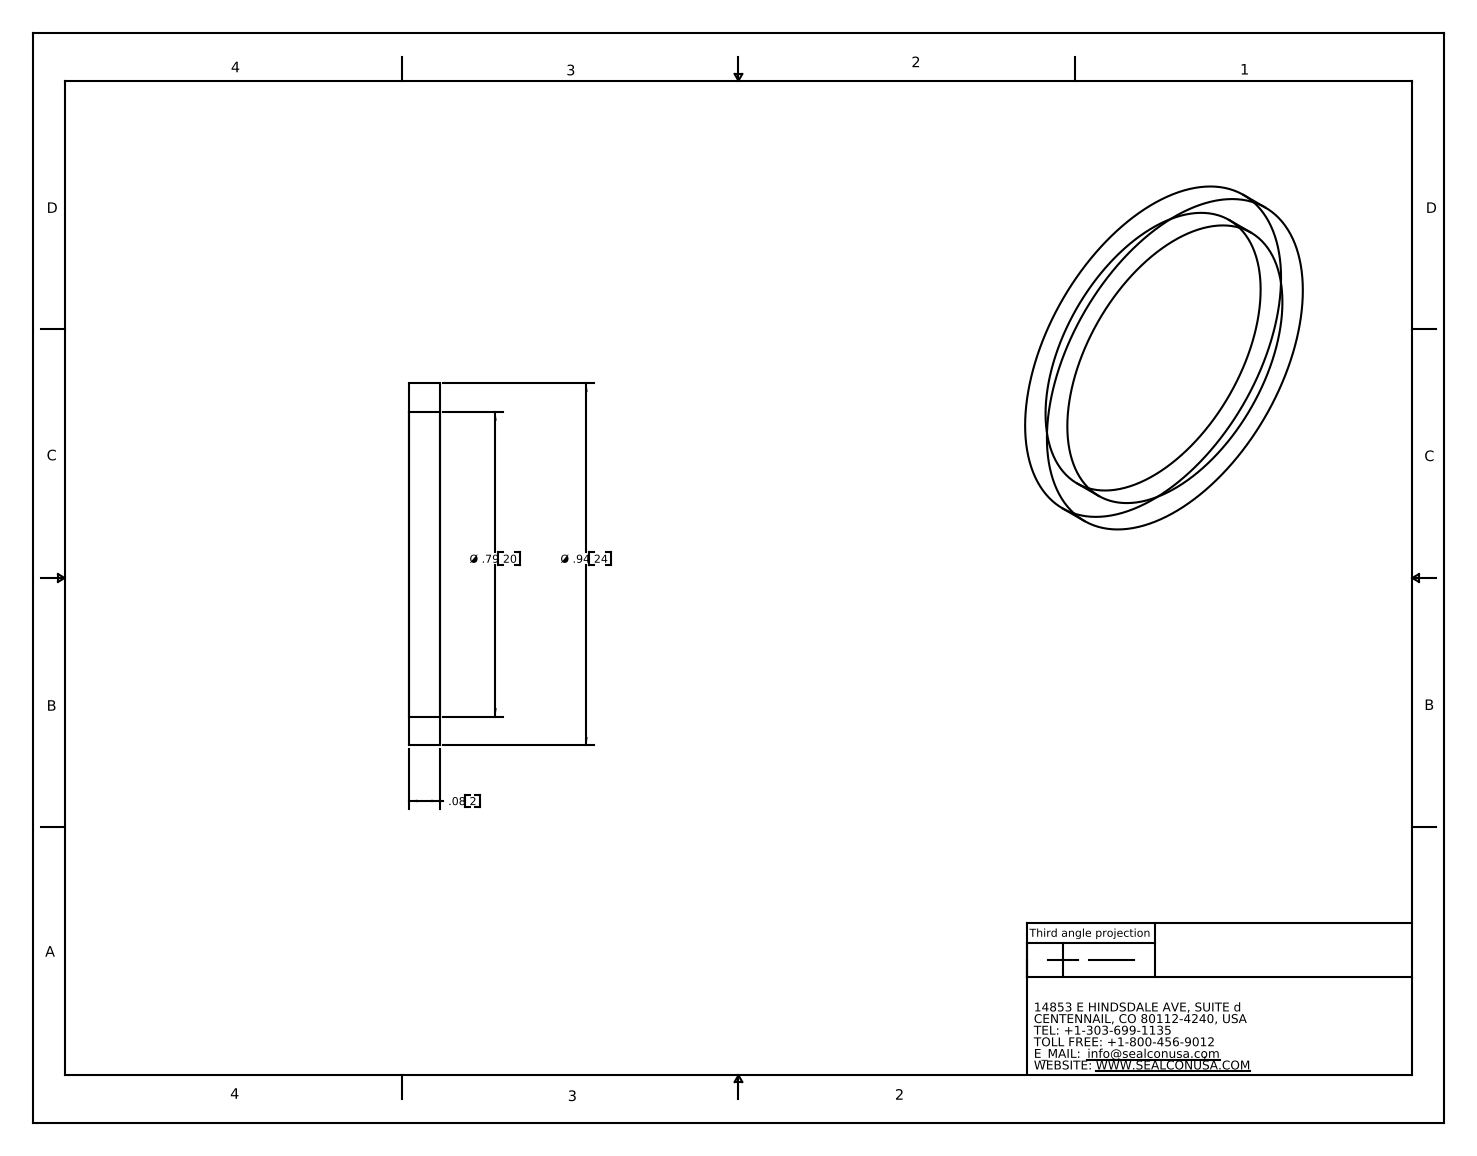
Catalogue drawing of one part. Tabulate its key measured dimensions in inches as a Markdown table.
| quantity | value |
| --- | --- |
| part name | MS-20-NY |
| STEP written by | SolidWorks 2007 (CONFIG_CONTROL_DESIGN) |
| units | inches |
| bodies | 1 solid, 6 faces (2 planar, 4 cylindrical, 0 other) |
| overall size | 0.94 × 0.94 × 0.08 |
| volume | 0.016 in³ |
| surface area | 0.842 in² |
| round holes (diameter × count) | 0.79 × 1 |
| round bosses / shafts (diameter × count) | 0.94 × 1 |
| main face-to-face distances | 0.08 |
